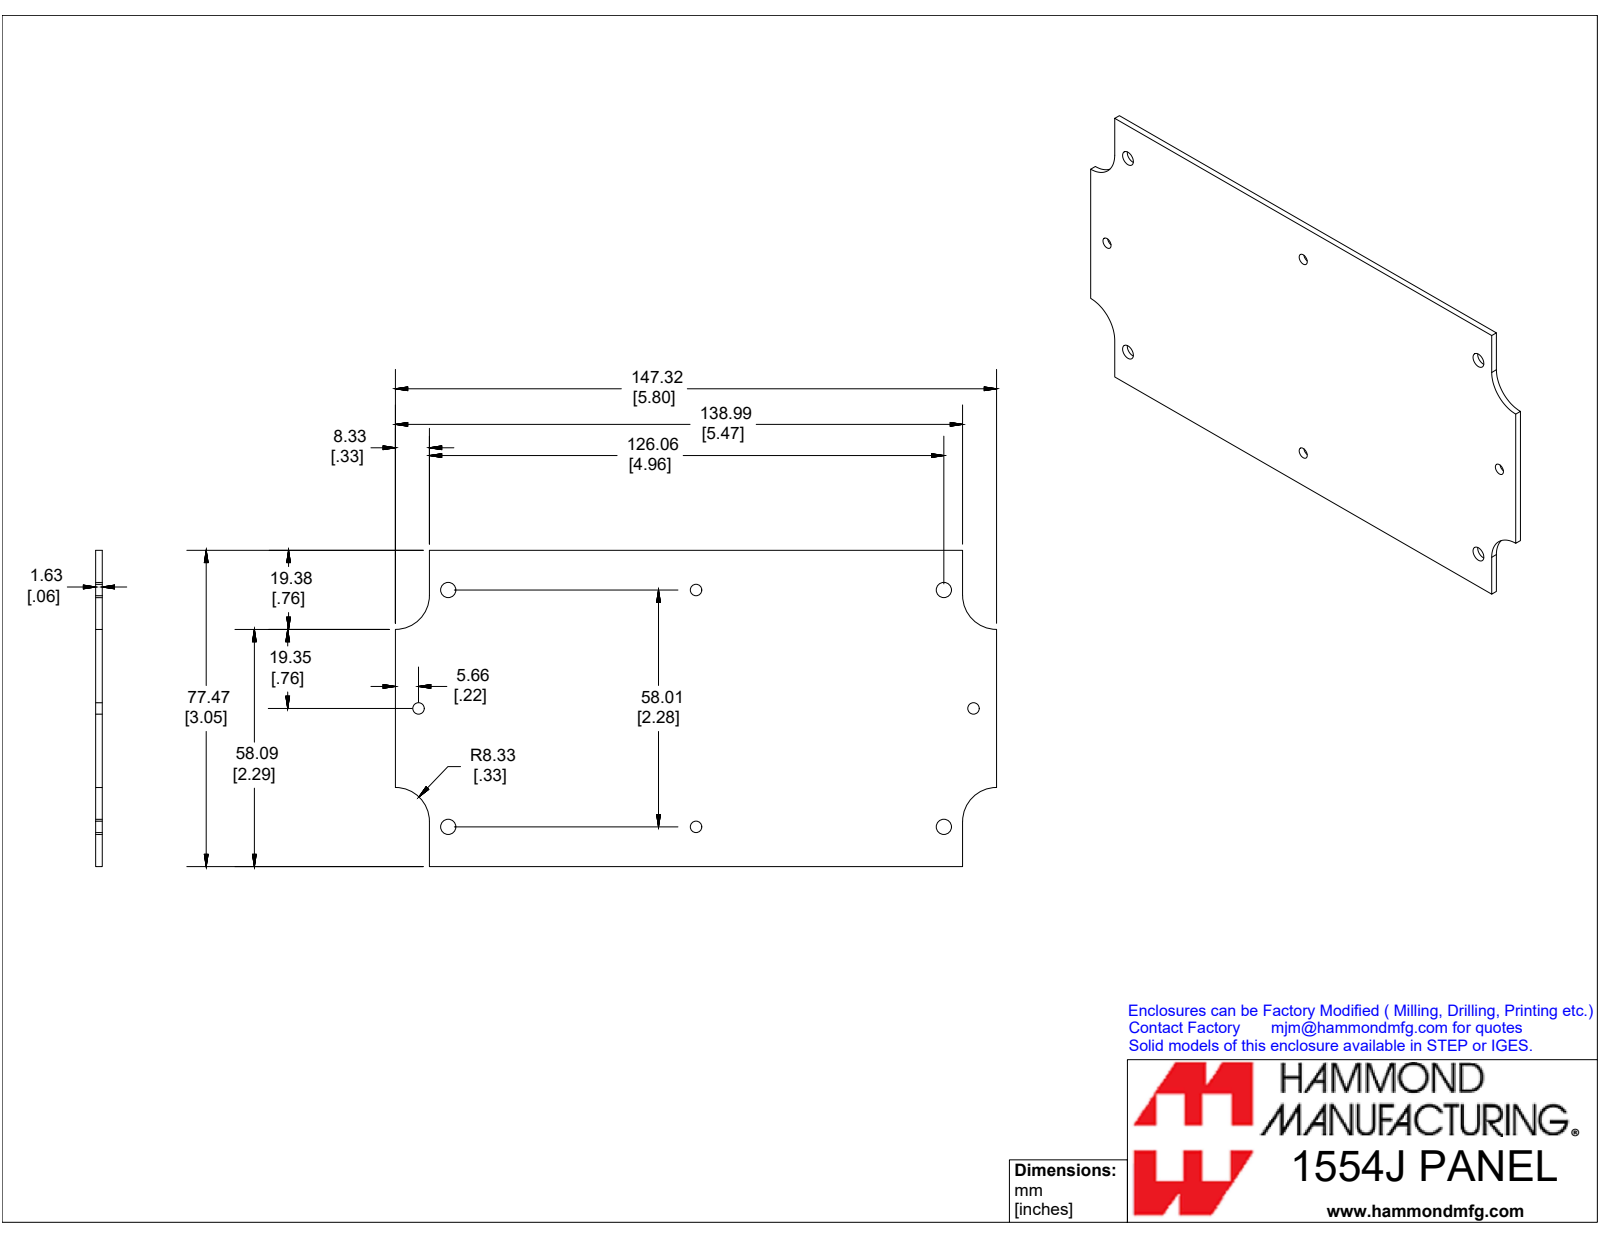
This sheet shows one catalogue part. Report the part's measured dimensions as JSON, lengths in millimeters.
{"part_name": "1554JPL", "step_written_by": "SolidWorks 2019 (CONFIG_CONTROL_DESIGN)", "units": "millimeters", "bodies": {"solids": 1, "faces": 22, "planar": 10, "cylindrical": 12, "other": 0}, "overall_size": [147.3, 77.5, 1.6], "volume_mm3": 17480, "surface_area_mm2": 22350, "round_holes": [[2.8, 4], [3.7, 4]], "partial_cylinders_radius": [[8.3, 4]], "face_to_face_distances": [1.6, 77.5, 8.3, 139, 147.3, 130.7], "hole_center_spacings": [29.9, 60.7, 73.9, 84, 132, 58, 121.5, 134.6]}
